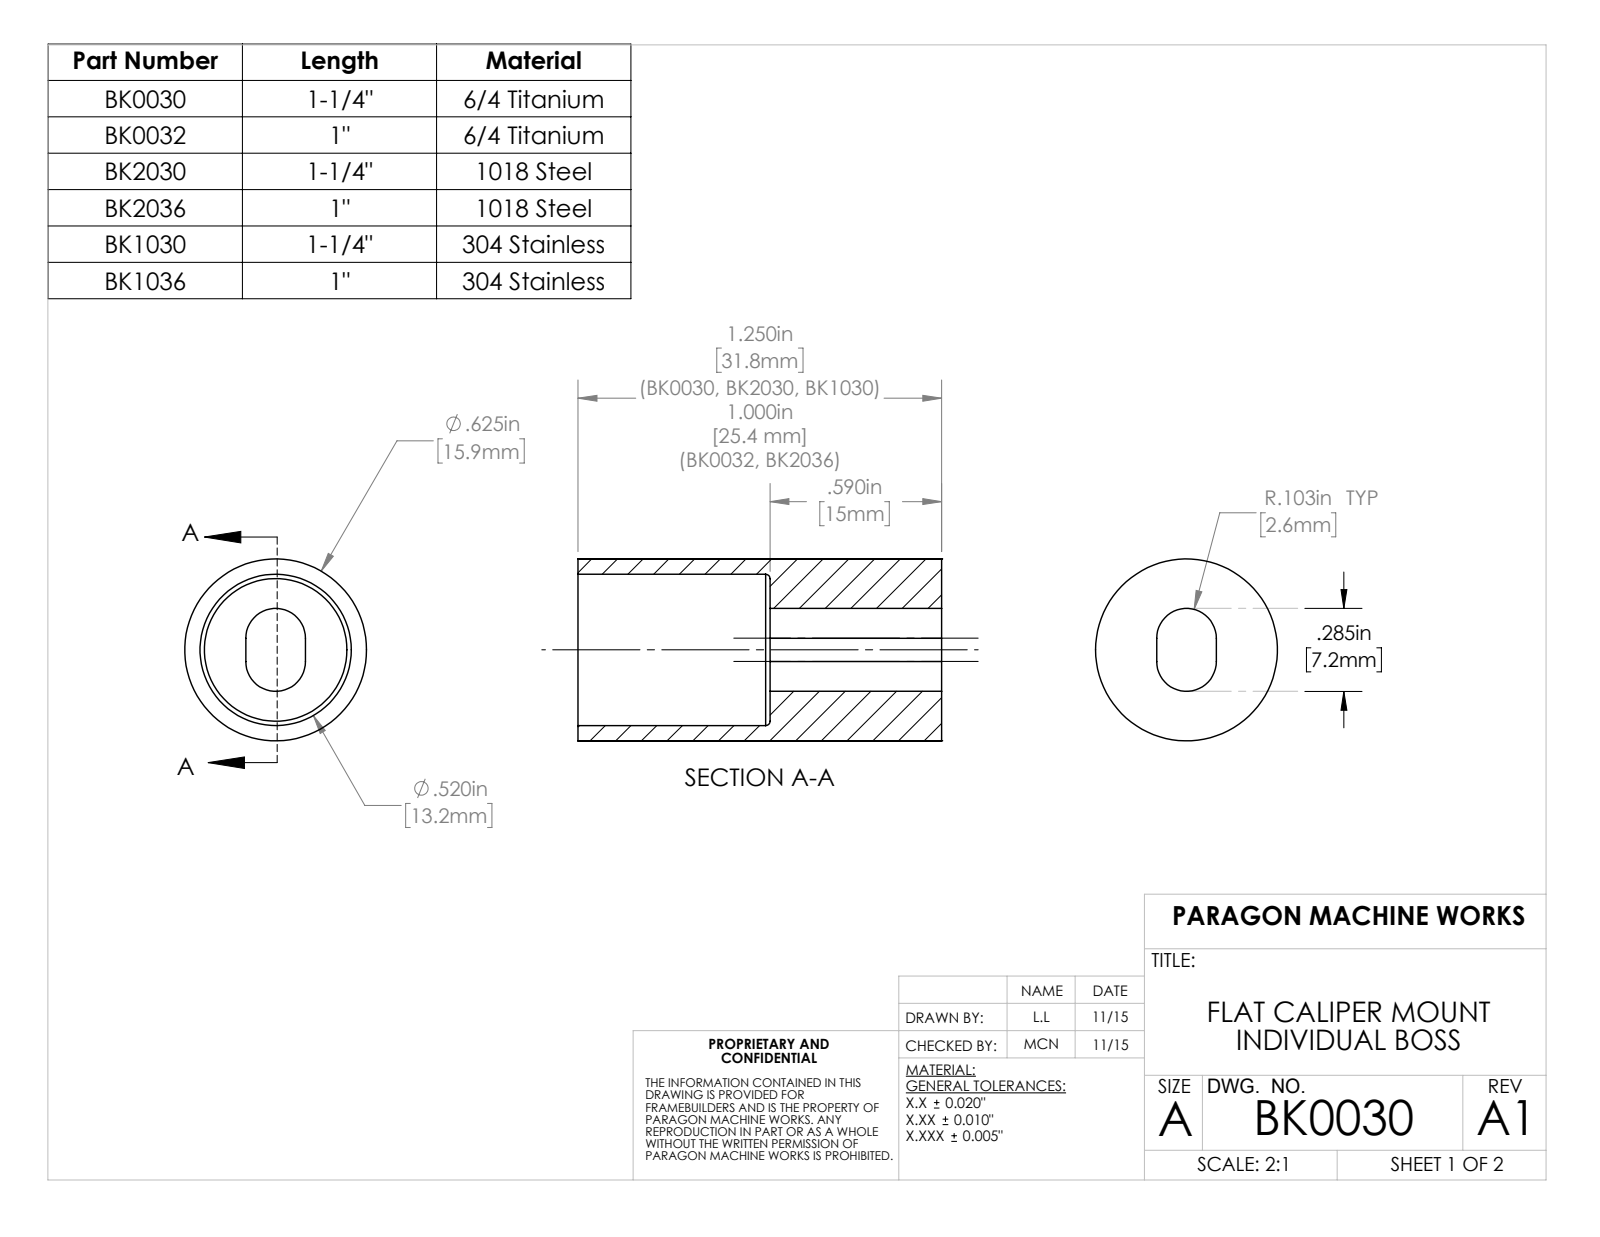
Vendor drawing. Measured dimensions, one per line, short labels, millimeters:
name: BK0030
written by: SolidWorks 2015 (AUTOMOTIVE_DESIGN)
unit: mm
bodies: 1 solid, 13 faces (5 planar, 6 cylindrical, 2 other)
size: 31.8 × 15.9 × 15.9
volume: 3 510 mm³; area: 2 910 mm²
holes: 1× ⌀13.2
bosses: 1× ⌀15.9
rounds: 2× R2.6
face distances: 15, 31.8, 16.8, 5.2
